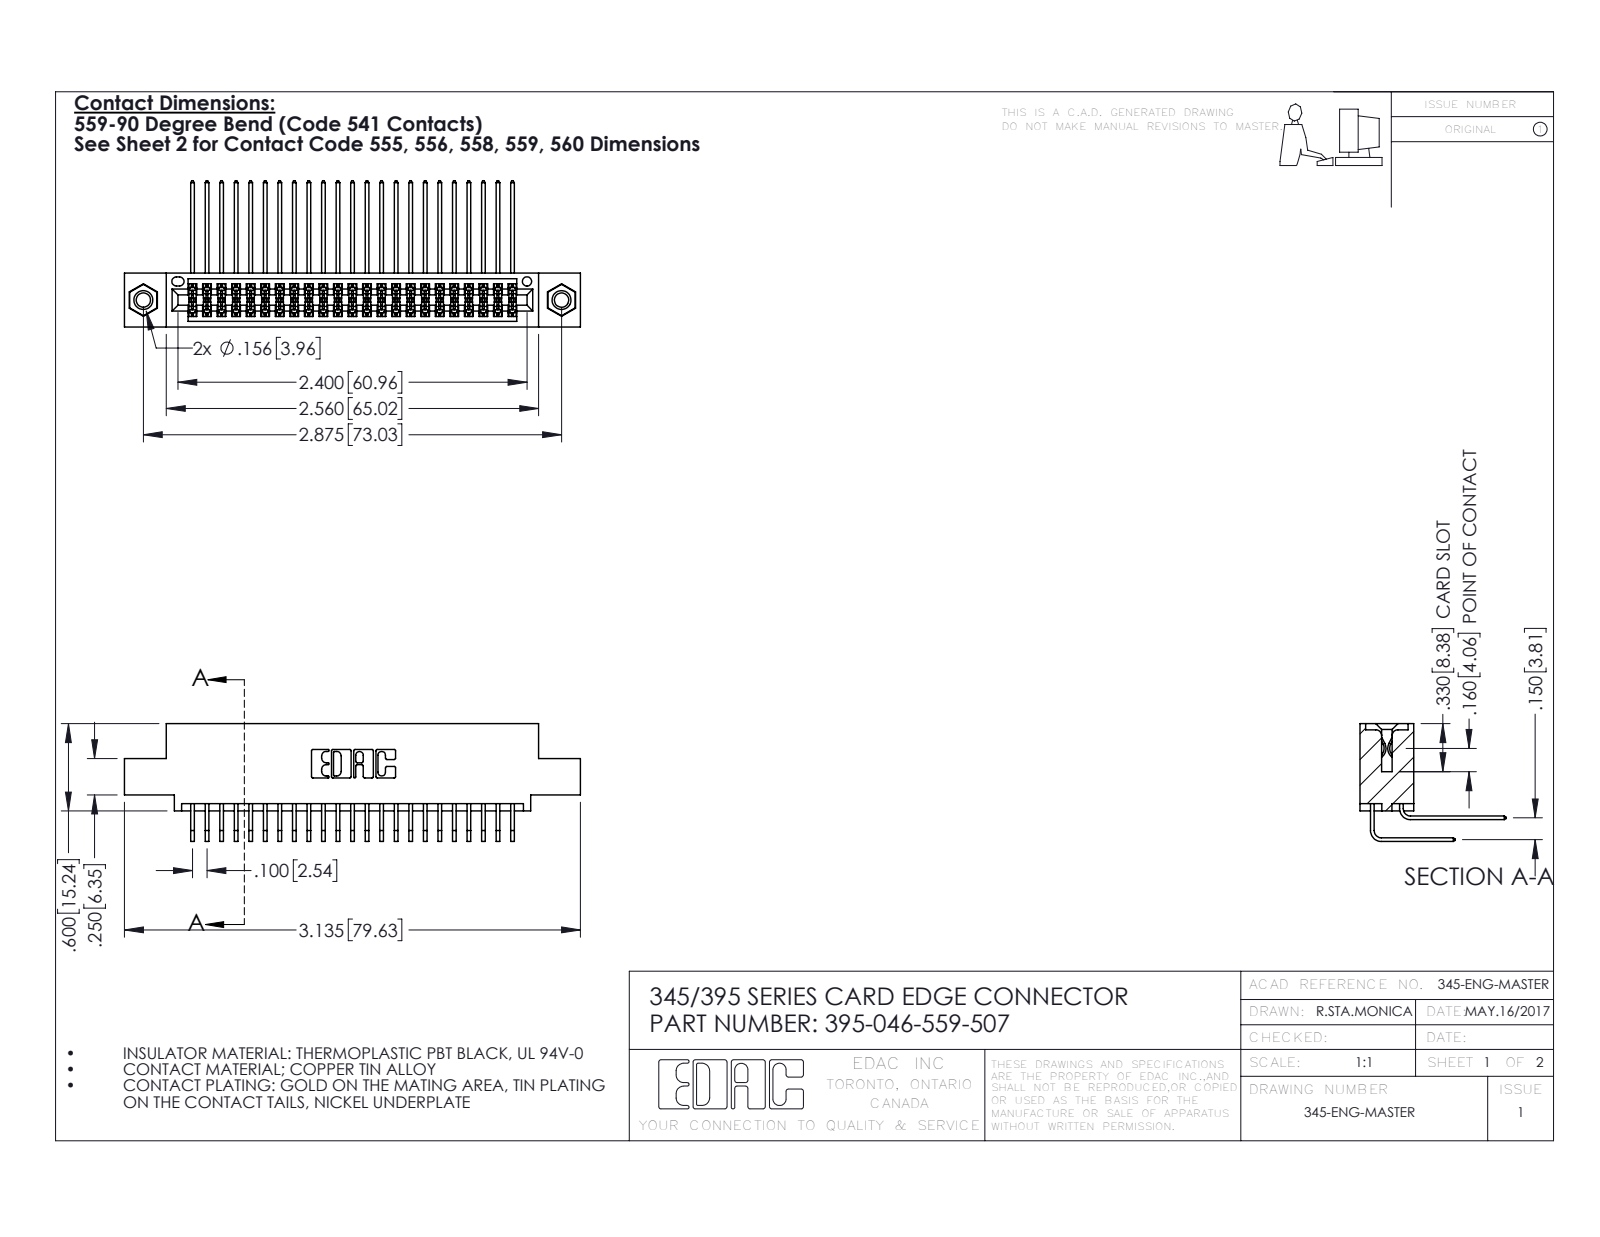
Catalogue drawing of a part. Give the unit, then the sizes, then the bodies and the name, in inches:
Units: inches
Overall size (bounding box): 3.135 × 1.005 × 0.809
Round holes (diameter × count): ⌀0.098 ×2, ⌀0.125 ×2, ⌀0.156 ×2, ⌀0.064 ×1
Round bosses / shafts (diameter × count): ⌀0.155 ×2
Partial cylindrical surfaces — rounded edges, fillets, slot ends (radius × count): R0.006 ×70, R0.01 ×22, R0.007 ×6, R0.031 ×6, R0.026 ×3, R0.014 ×2, R0.019 ×2, R0.022 ×2
Main face-to-face distances: 0.072, 0.298, 0.2, 0.37, 0.098, 0.272, 0.025, 0.225, 0.15, 0.175
Hole centre spacings: 0.27, 2.641, 2.875
Volume: 0.472 in³ · Surface area: 19.28 in²
Bodies: 49 solids, 2582 faces (1726 planar, 840 cylindrical, 16 other)
Part name (STEP PRODUCT): 345-250-001_345-250-005-103; 345 Part_0.110 Offset - 0.156 Dia-TI; 345-292-001_559 Tail - 2; 395-046-559-507 (+1 more)
STEP written by: SolidWorks 2016 (CONFIG_CONTROL_DESIGN)
